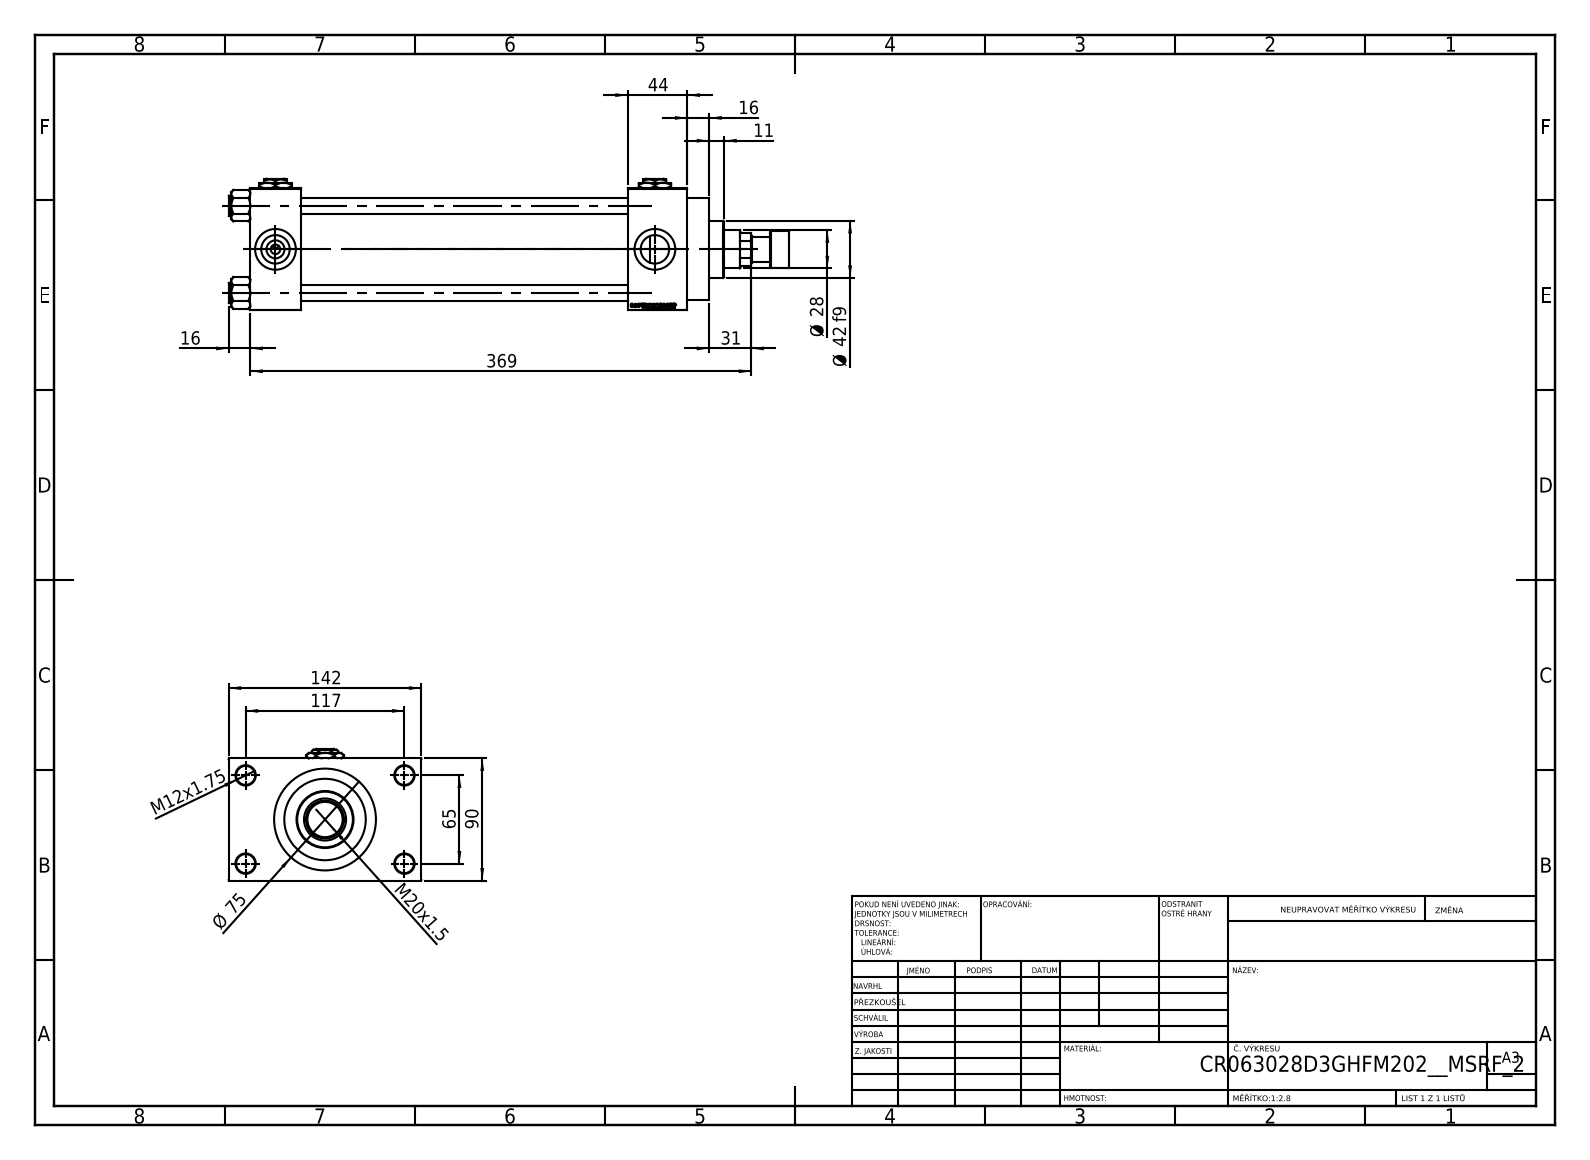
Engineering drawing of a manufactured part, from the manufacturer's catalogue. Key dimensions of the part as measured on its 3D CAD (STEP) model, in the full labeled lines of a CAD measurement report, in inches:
Part name (STEP PRODUCT): V215CR_ROD_END_F; V215CR_D_Body; V215_VC_A; Zatka_pro_OIL_PORT (+3 more)
STEP written by: SolidWorks 2019 (CONFIG_CONTROL_DESIGN)
Units: inches
Bodies: 14 solids, 1218 faces (549 planar, 103 cylindrical, 566 other)
Overall size (bounding box): 16.26 × 5.591 × 3.819
Volume: 86.04 in³ · Surface area: 507 in²
Round holes (diameter × count): ⌀0.472 ×4, ⌀0.551 ×4, ⌀0.825 ×4, ⌀1.181 ×4, ⌀0.276 ×3, ⌀0.728 ×1, ⌀1.102 ×1, ⌀1.22 ×1, ⌀1.969 ×1, ⌀2.362 ×1, ⌀2.48 ×1
Round bosses / shafts (diameter × count): ⌀0.591 ×4, ⌀2.953 ×1, ⌀2.717 ×1, ⌀1.654 ×1, ⌀1.063 ×1, ⌀0.709 ×1
Main face-to-face distances: 3.543, 9.488, 1.457, 10.945, 11.22, 12.677, 1.732, 1.024, 4.567, 0.63
Hole centre spacings: 1.037, 1.79, 2.531, 2.635, 2.748, 3.569, 4.383, 2.559
